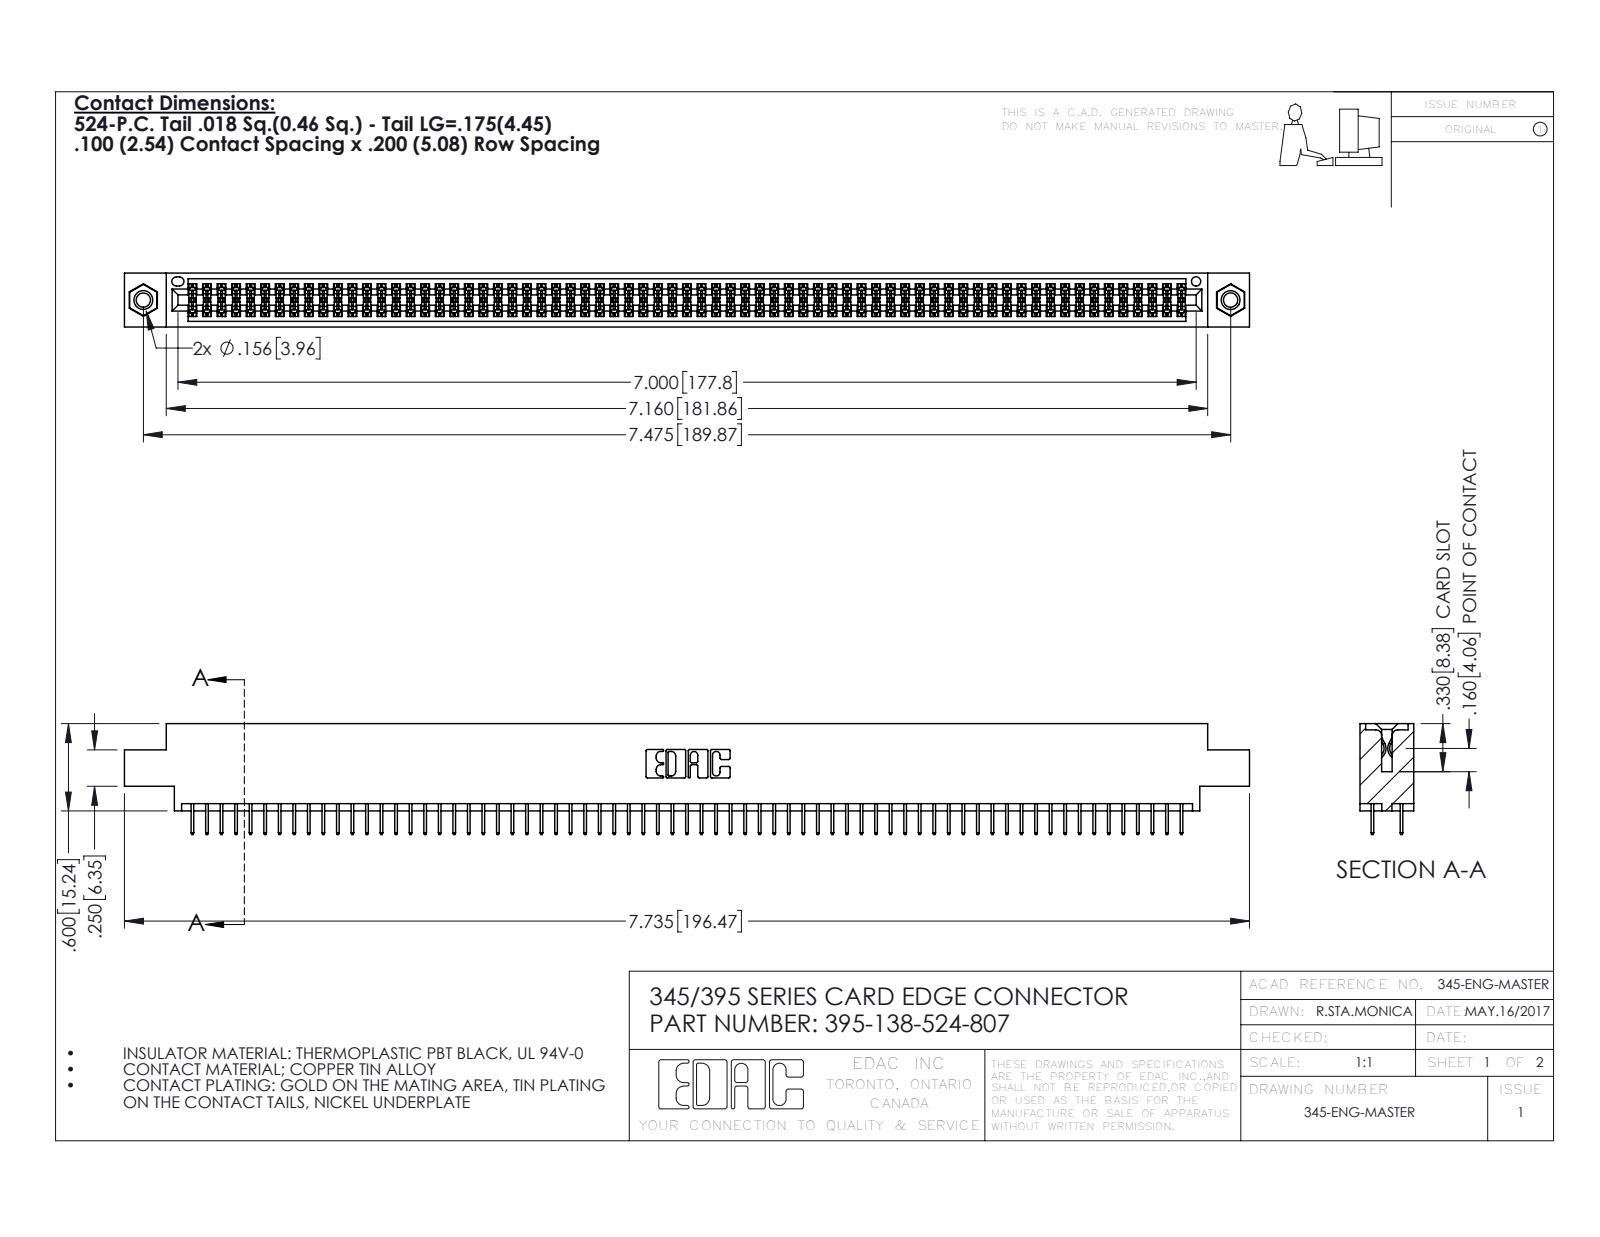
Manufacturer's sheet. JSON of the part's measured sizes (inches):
{"part_name": "345-292-001_345-293-124; 345-250-001_345-250-005-103; 345 Part_0.170 Offset - 0.156 Dia-TI; 395-138-524-807", "step_written_by": "SolidWorks 2016 (CONFIG_CONTROL_DESIGN)", "units": "inches", "bodies": {"solids": 141, "faces": 7642, "planar": 5498, "cylindrical": 2128, "other": 16}, "overall_size": [7.735, 0.762, 0.37], "volume_in3": 1.159, "surface_area_in2": 43.75, "round_holes": [[0.098, 2], [0.125, 2], [0.156, 2], [0.064, 1]], "round_bosses_or_shafts": [[0.155, 2]], "partial_cylinders_radius": [[0.006, 207], [0.01, 22], [0.007, 6], [0.031, 6], [0.026, 3], [0.014, 2], [0.019, 2], [0.022, 2]], "face_to_face_distances": [0.072, 0.298, 0.2, 0.37, 0.098, 0.272, 0.025, 0.225, 0.072, 0.175], "hole_center_spacings": [0.27, 7.239, 7.475]}
